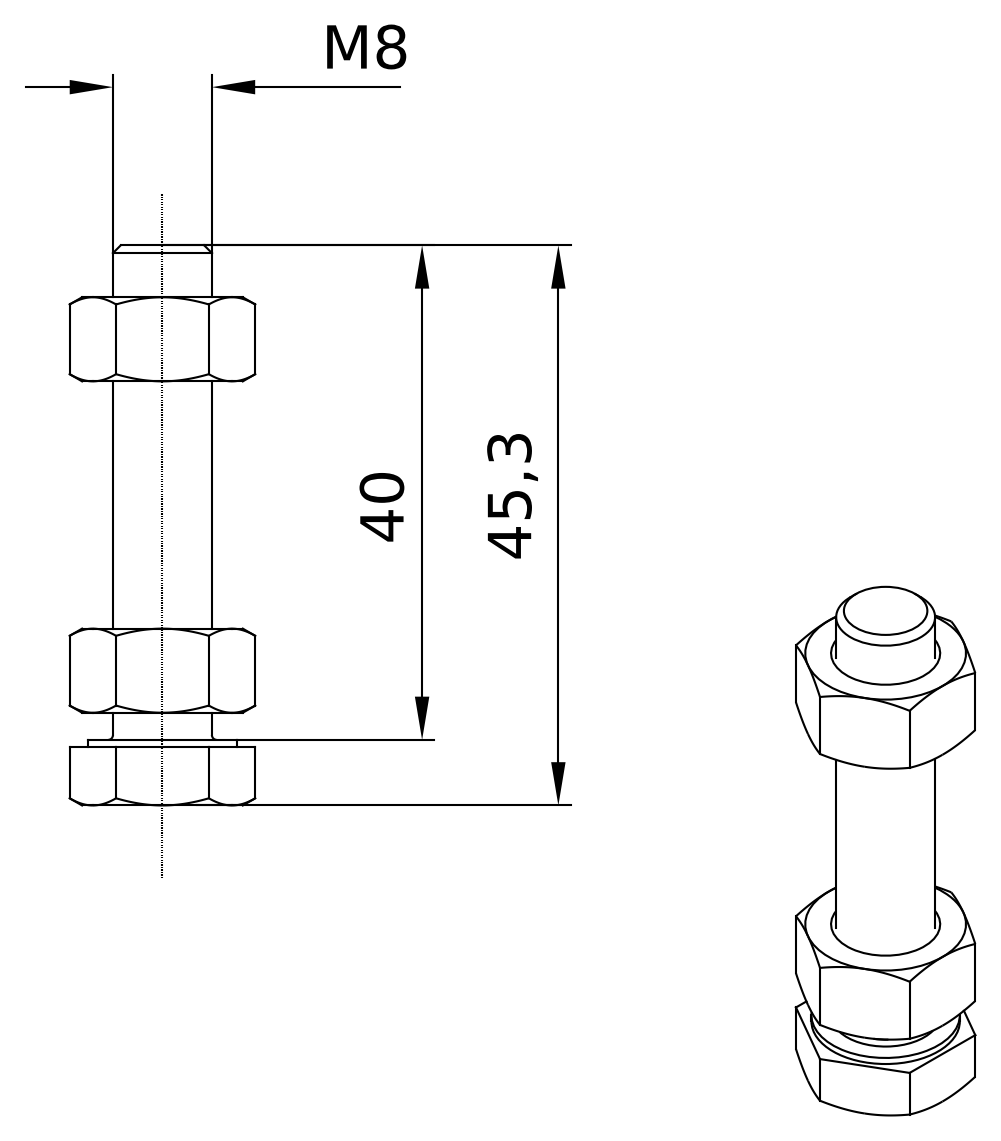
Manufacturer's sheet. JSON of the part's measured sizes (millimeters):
{"step_written_by": "Autodesk Inventor 8 (AUTOMOTIVE_DESIGN)", "units": "millimeters", "bodies": {"solids": 1, "faces": 86, "planar": 26, "cylindrical": 8, "other": 52}, "overall_size": [45.3, 15.01, 13], "volume_mm3": 4049, "surface_area_mm2": 2198, "round_bosses_or_shafts": [[12, 1], [8, 1]], "face_to_face_distances": [13, 6.8, 26.8, 20, 34.3, 14.3, 7.5, 33.6, 41.1, 35.8]}
